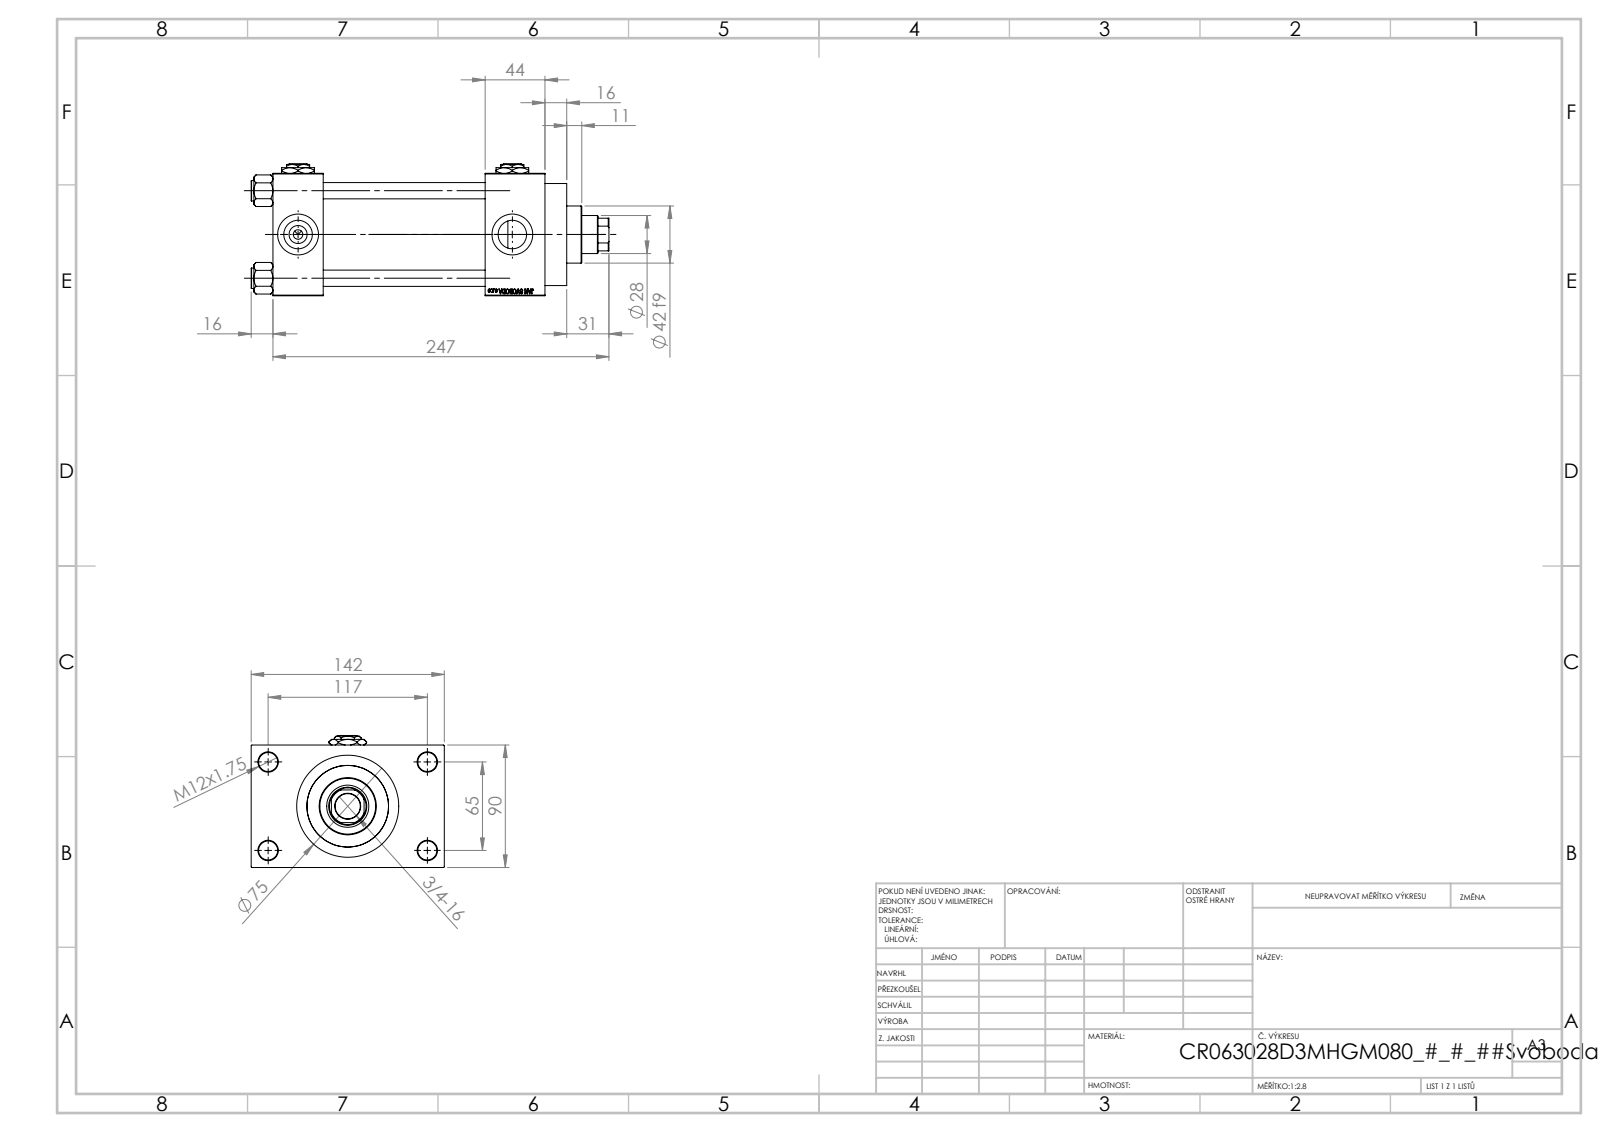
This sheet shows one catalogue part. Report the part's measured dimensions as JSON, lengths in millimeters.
{"part_name": "V215CR_VCP_D; V215CR_D_TYCINKA; NUT_M5_D; V215_VC_A (+2 more)", "step_written_by": "SolidWorks 2019 (CONFIG_CONTROL_DESIGN)", "units": "millimeters", "bodies": {"solids": 13, "faces": 1204, "planar": 545, "cylindrical": 99, "other": 560}, "overall_size": [263, 142, 97], "volume_mm3": 1192000, "surface_area_mm2": 244149, "round_holes": [[12, 4], [14, 4], [20.96, 4], [30, 4], [7, 3], [18.5, 1], [28, 1], [31, 1], [50, 1], [60, 1], [63, 1]], "round_bosses_or_shafts": [[15, 4], [75, 1], [69, 1], [42, 1]], "partial_cylinders_radius": [[13.5, 1]], "face_to_face_distances": [90, 119, 37, 156, 163, 200, 44, 26, 116, 16], "hole_center_spacings": [26.35, 45.47, 64.3, 66.92, 69.81, 90.65, 111.34, 65]}
